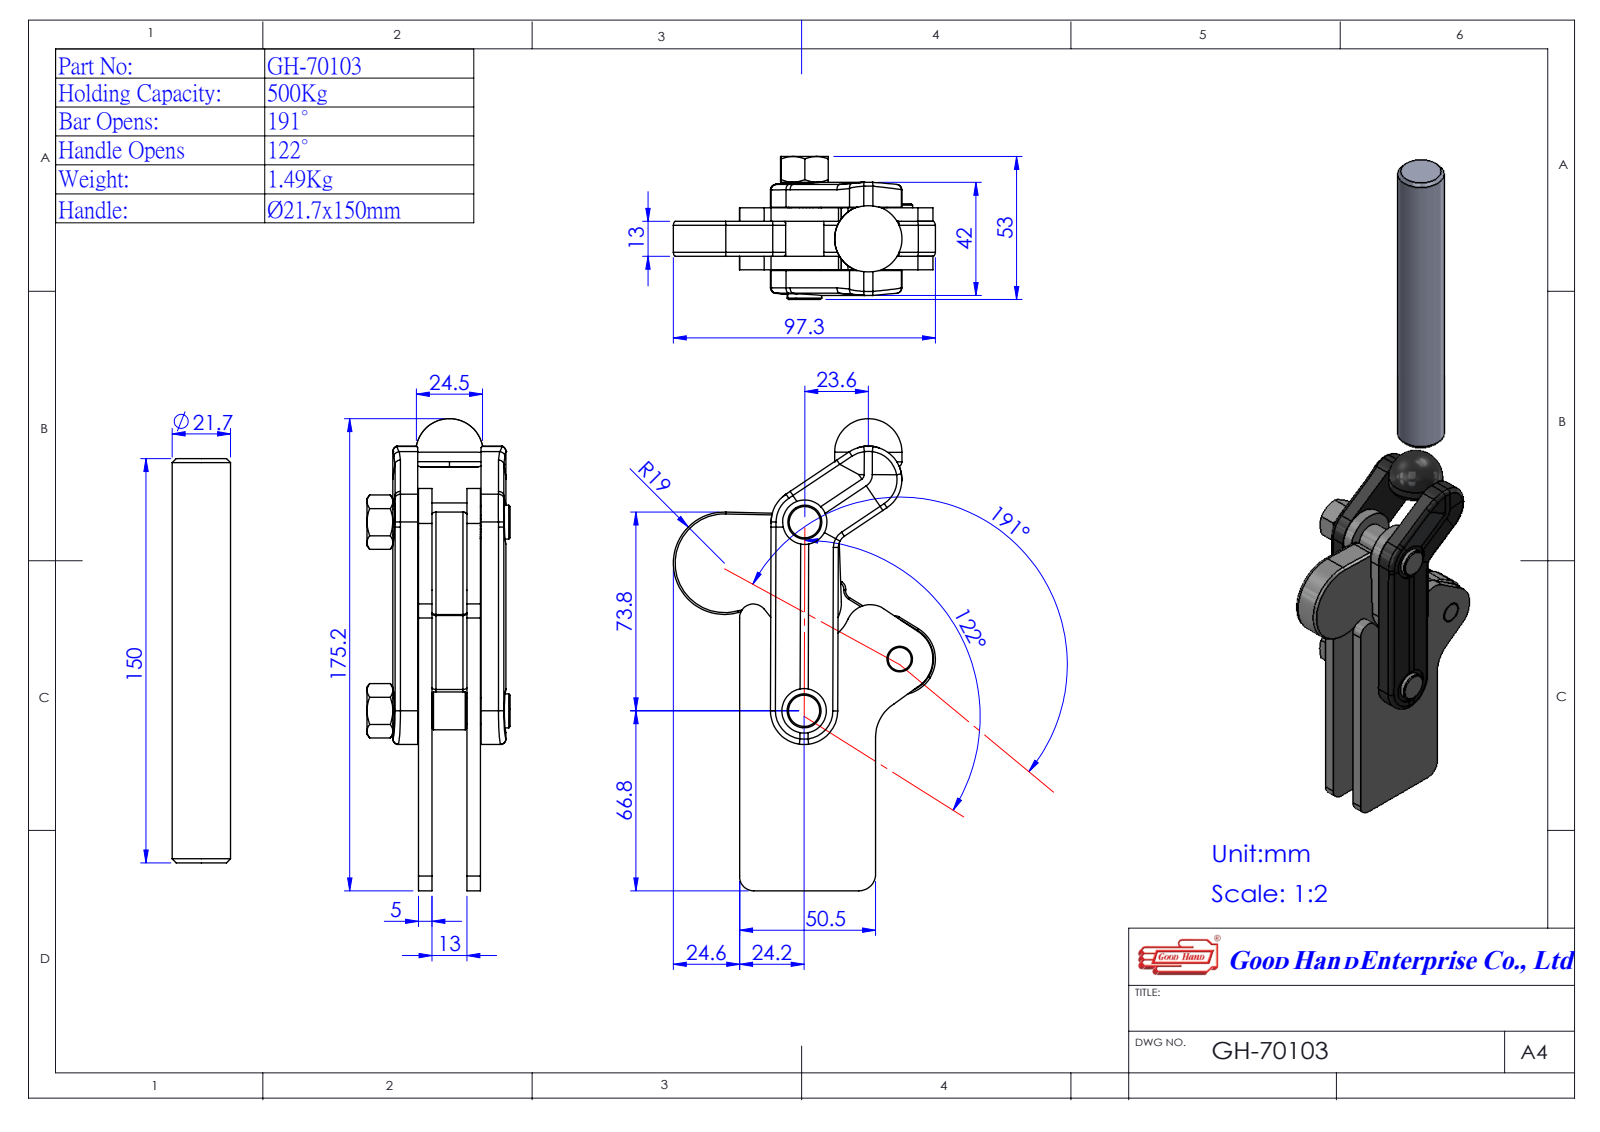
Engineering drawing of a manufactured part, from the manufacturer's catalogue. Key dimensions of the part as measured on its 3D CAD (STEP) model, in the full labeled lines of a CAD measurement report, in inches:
Part name (STEP PRODUCT): Group5^GH-70103(簡化)-1; Group2^GH-70103(簡化)-1; Group1^GH-70103(簡化)-1; GH-70103(簡化)-1 (+2 more)
STEP written by: SolidWorks 2016 (AUTOMOTIVE_DESIGN)
Units: inches
Bodies: 5 solids, 230 faces (101 planar, 99 cylindrical, 30 other)
Overall size (bounding box): 12.842 × 3.831 × 2
Volume: 11.73 in³ · Surface area: 127.7 in²
Round holes (diameter × count): ⌀0.374 ×4, ⌀0.665 ×1
Round bosses / shafts (diameter × count): ⌀0.375 ×4, ⌀0.496 ×2, ⌀0.854 ×1, ⌀0.559 ×1
Partial cylindrical surfaces — rounded edges, fillets, slot ends (radius × count): R0.059 ×12, R0.118 ×4, R0.492 ×4, R0.197 ×3, R0.201 ×1, R0.207 ×1, R0.248 ×1, R0.354 ×1
Main face-to-face distances: 0.197, 0.709, 0.512, 0.236, 0.748, 0.039, 0.945, 0.906, 0.325, 0.364
Hole centre spacings: 1.181, 1.575, 1.576, 1.589, 2.431, 2.756
